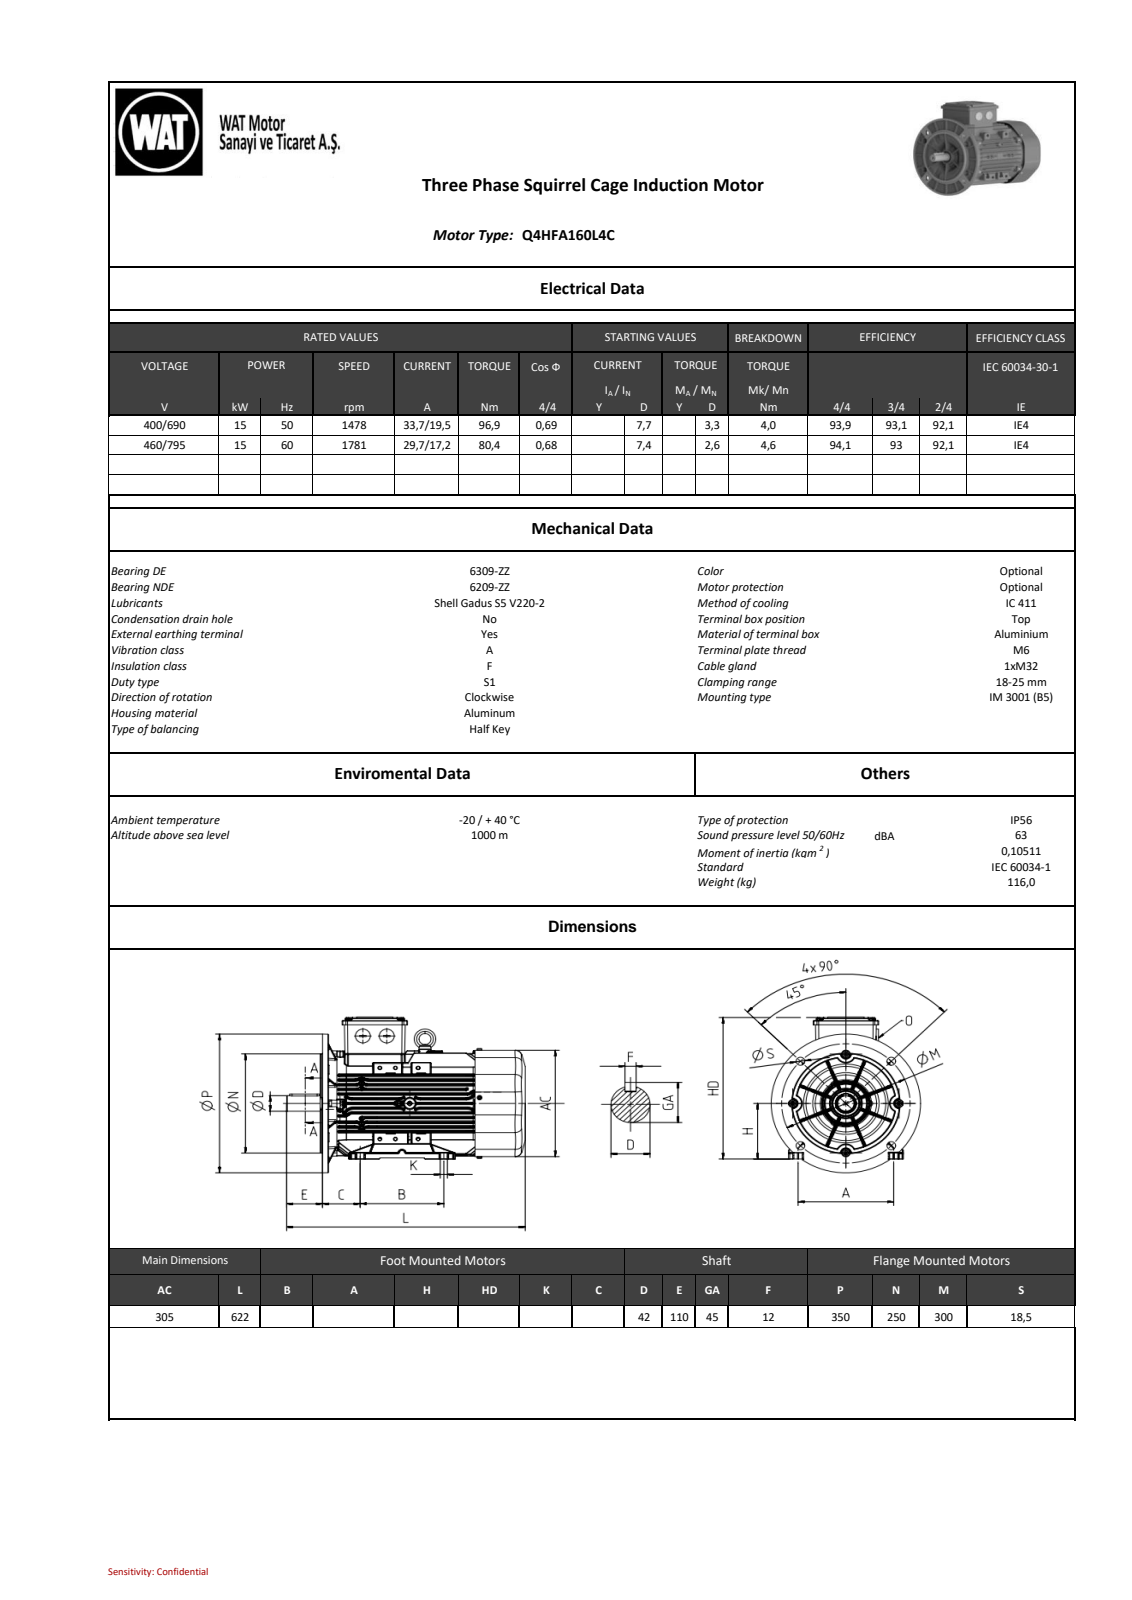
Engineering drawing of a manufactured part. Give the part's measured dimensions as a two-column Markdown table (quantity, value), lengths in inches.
| quantity | value |
| --- | --- |
| part name | AA_objects |
| STEP written by | SIEMENS PLM Software NX2206.8101 (AP203_CONFIGURATION_CONTROLLED_3D_DESIGN_OF_MECHANICAL_PARTS_AND_ASSEMBLIES_MIM_LF) |
| units | inches |
| bodies | 0 solids, 6928 faces (1914 planar, 2534 cylindrical, 2480 other) |
| overall size | 24.367 × 15.463 × 13.78 |
| round holes (diameter × count) | 0.591 × 4, 0.394 × 1, 0.551 × 1, 0.669 × 1, 2.835 × 1, 3.371 × 1, 3.701 × 1, 4.488 × 1, 5.276 × 1, 6.063 × 1, 6.85 × 1, 7.638 × 1 |
| round bosses / shafts (diameter × count) | 0.315 × 4, 1.496 × 2, 10.728 × 1, 9.843 × 1, 7.008 × 1, 6.22 × 1, 5.433 × 1, 4.646 × 1 |
| partial cylindrical surfaces (radius × count) | 0.02 × 689, 0.039 × 300, 0.079 × 130, 0.059 × 116, 0.157 × 76, 0.197 × 54, 0.098 × 43, 0.118 × 28 |
| main face-to-face distances | 5.669, 6.614, 4.724, 0.469, 0.379, 0.581, 6.63, 6.251, 0.96, 0.467 |
| hole center spacings | 5.61, 7.934, 11.22, 0.017, 5.597, 5.6, 5.604, 5.607 |
